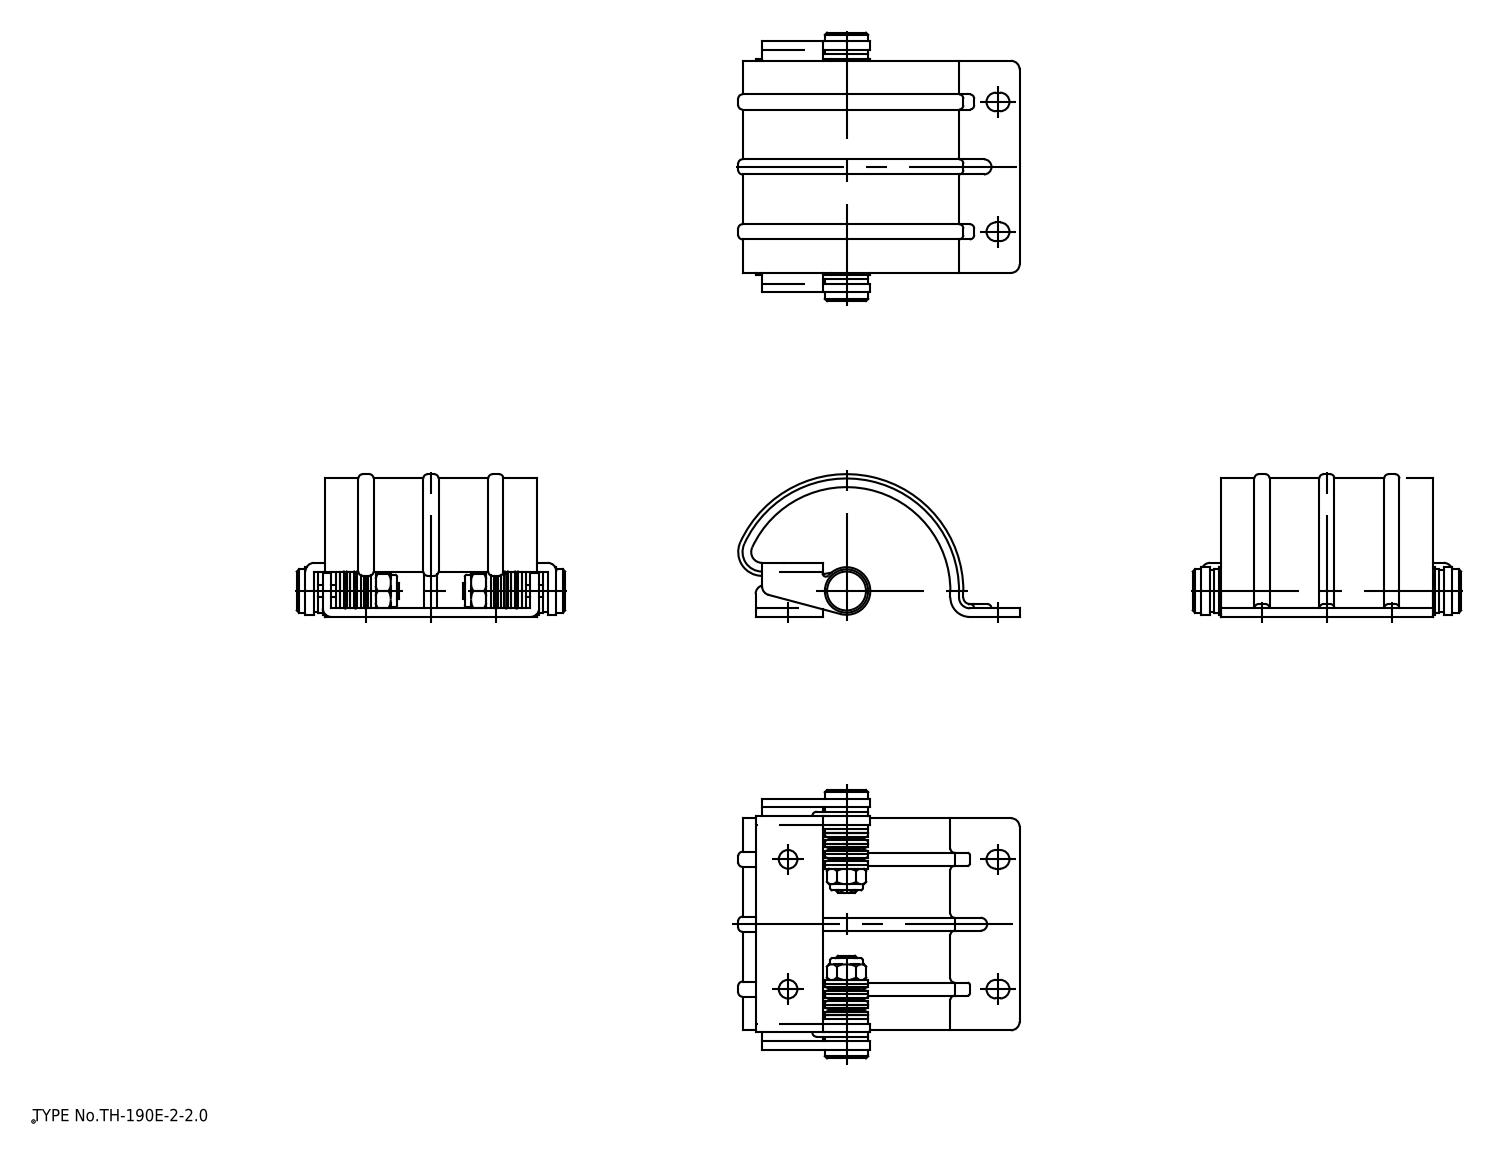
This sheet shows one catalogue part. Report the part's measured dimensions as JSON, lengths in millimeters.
{"part_name": "ヒンジピース(B); ヒンジピース(A)", "step_written_by": "spGate 20.6.3 (****-****-****-****) (AUTOMOTIVE_DESIGN)", "units": "millimeters", "bodies": {"solids": 2, "faces": 454, "planar": 120, "cylindrical": 172, "other": 162}, "overall_size": [65.03, 62, 33], "volume_mm3": 16420, "surface_area_mm2": 17570, "round_holes": [[4.3, 2]], "round_bosses_or_shafts": [[10, 1], [9.9, 1], [9.8, 1], [7.5, 1]], "partial_cylinders_radius": [[1, 37], [2, 8], [0.75, 7], [0.5, 4], [2.15, 4], [2.5, 3], [3.5, 2], [4.5, 2]], "face_to_face_distances": [2, 10.5, 1, 4, 3, 49, 8.5, 52, 1.5, 12.5], "hole_center_spacings": [30]}
